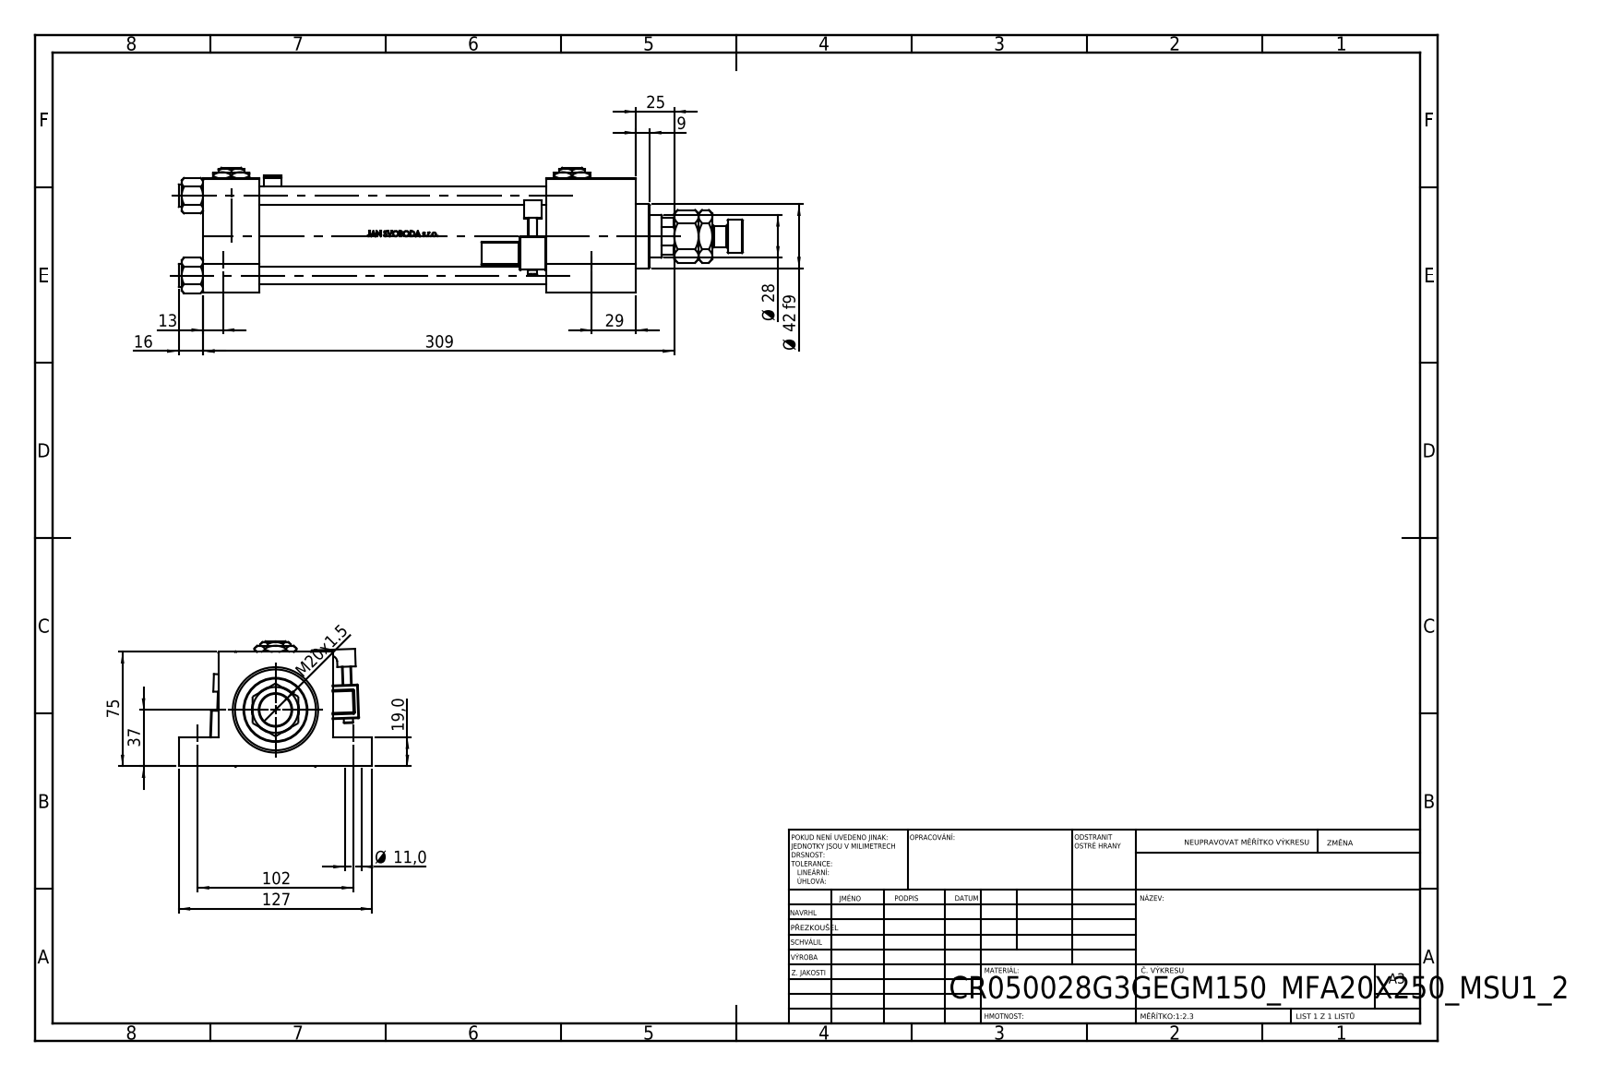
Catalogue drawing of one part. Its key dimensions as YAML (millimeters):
part_name: "NUT_M5_G; V215_VC_A; MFA; V215CR_G_TYCINKA (+4 more)"
step_written_by: "SolidWorks 2019 (CONFIG_CONTROL_DESIGN)"
units: millimeters
bodies: {solids: 16, faces: 1378, planar: 550, cylindrical: 188, other: 640}
overall_size: [370, 127, 82.27]
volume: 1043000
surface_area: 258127
round_holes:
  - {diameter: 11, count: 4}
  - {diameter: 12, count: 4}
  - {diameter: 7, count: 2}
  - {diameter: 20.96, count: 2}
  - {diameter: 30, count: 2}
  - {diameter: 18.5, count: 1}
  - {diameter: 28, count: 1}
  - {diameter: 31, count: 1}
  - {diameter: 41, count: 1}
  - {diameter: 50, count: 1}
  - {diameter: 53, count: 1}
round_bosses_or_shafts:
  - {diameter: 15, count: 4}
  - {diameter: 6, count: 2}
  - {diameter: 56, count: 1}
  - {diameter: 42, count: 1}
  - {diameter: 22, count: 1}
  - {diameter: 14, count: 1}
partial_cylinders:
  - {radius: 0.5, count: 48}
  - {radius: 1, count: 2}
  - {radius: 2.5, count: 2}
  - {radius: 4, count: 2}
  - {radius: 6, count: 1}
  - {radius: 13.5, count: 1}
face_to_face_distances: [75, 37, 284, 247, 225, 188, 59, 56, 19, 26]
hole_center_spacings: [52.3, 36.63, 37.34, 51.3, 52.63, 73.96, 102, 234.61]
